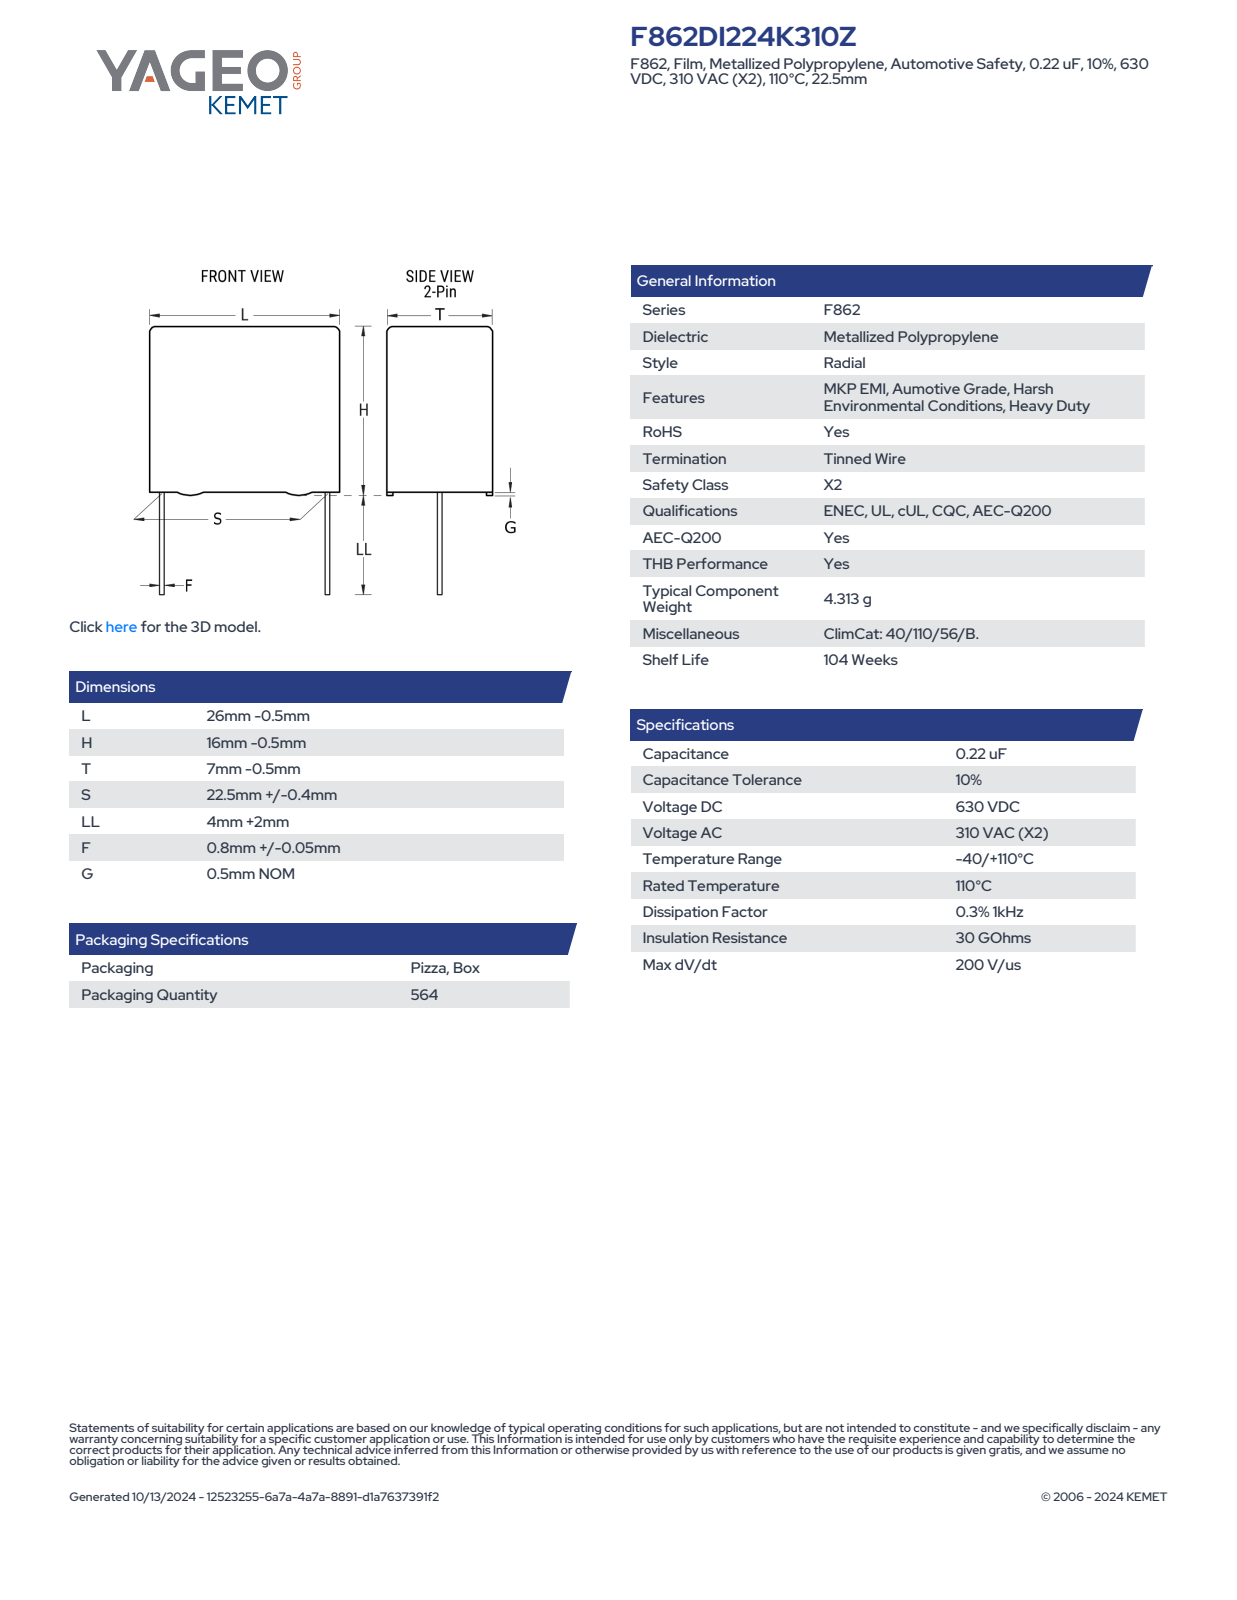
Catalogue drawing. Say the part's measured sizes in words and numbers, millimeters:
The part is named "CFR_RBG_26X16X7_L25.5H15.5T6.5S22.5LL6F0.85G0.5". Its 3-D file was written by "SolidWorks 2014 (AUTOMOTIVE_DESIGN)". It is 4 solids with 89 faces: 81 planar, 8 cylindrical and 0 other. Overall it measures 25.5 by 21.5 by 6.5 millimeters. Its volume is 2 493 cubic millimeters and its surface area 1 400 square millimeters. Round bosses or shafts: 2 of diameter 0.85. Partial cylindrical surfaces (rounded edges, fillets, slot ends): 4 of radius 0.5. The main face-to-face distances are 6.5, 15, 25.5, 0.37, 6.13, 0.5, 15.5, 5.76, 6, 21.5.
